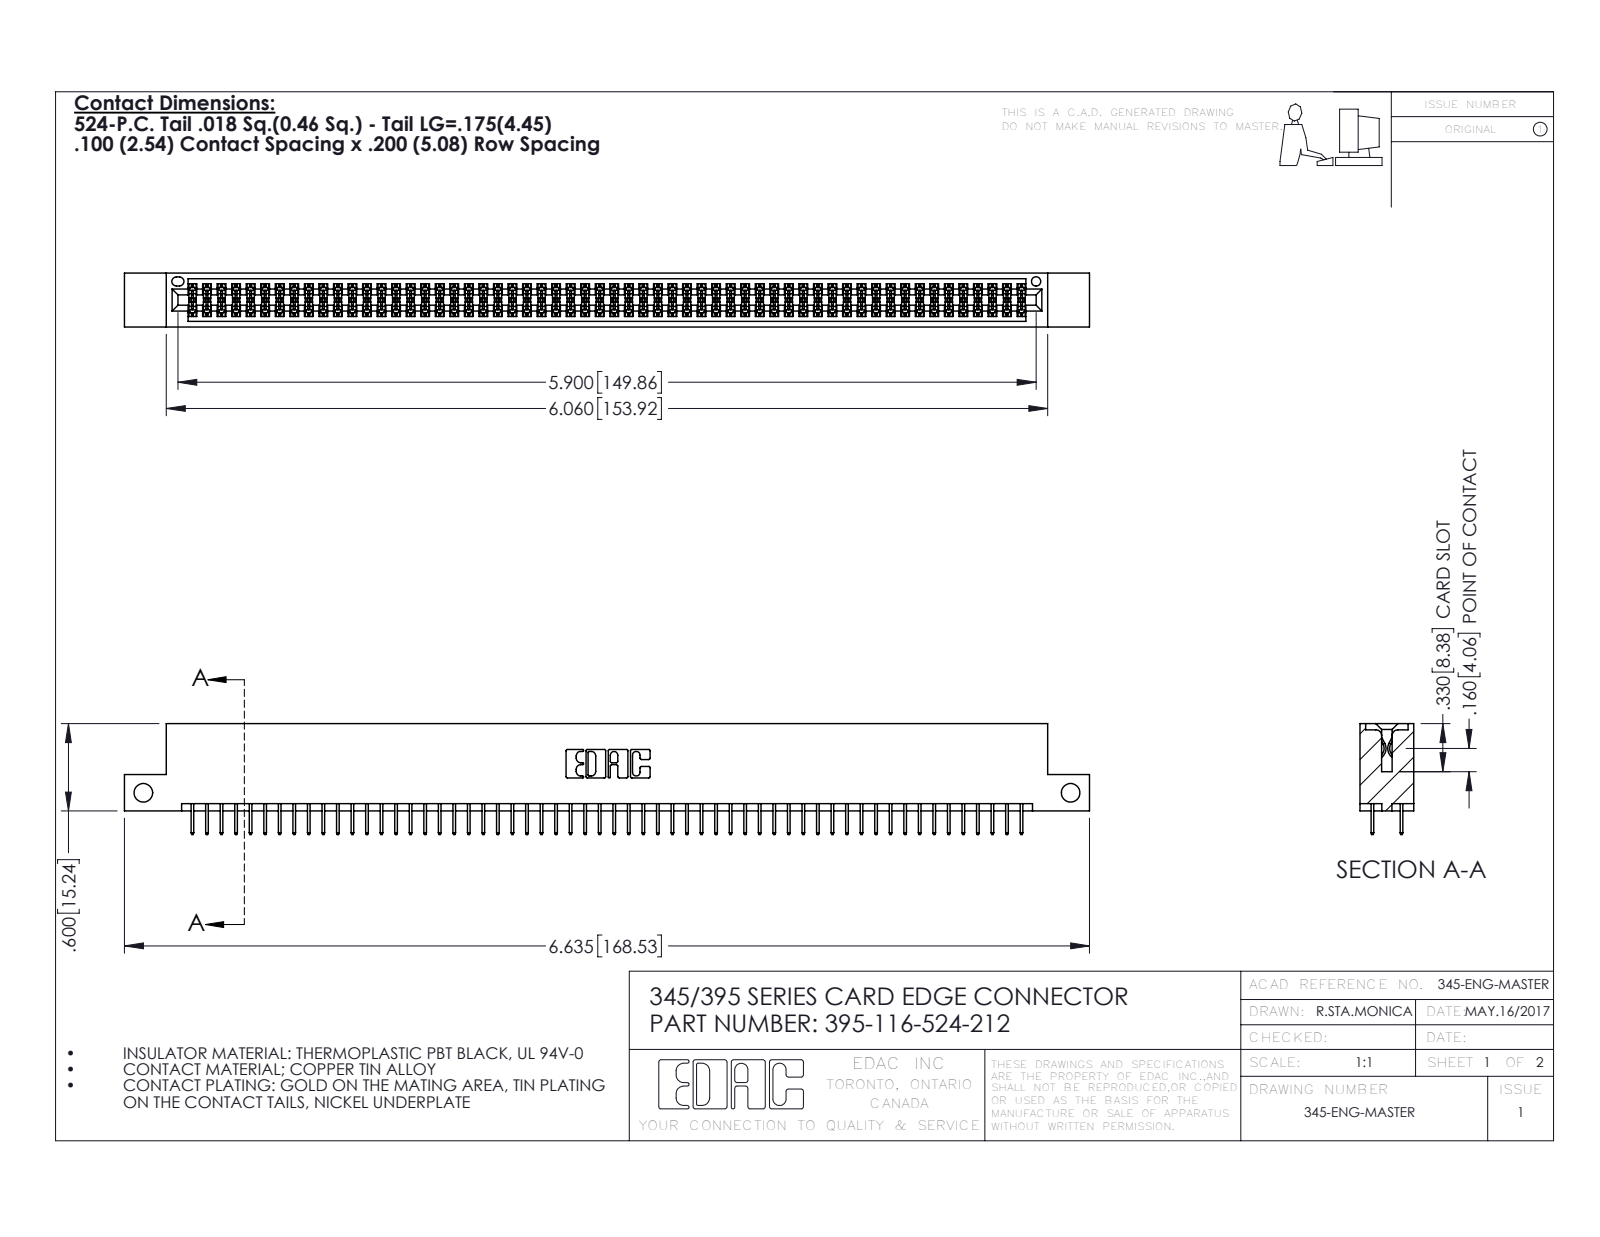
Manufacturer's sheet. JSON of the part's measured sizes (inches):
{"part_name": "345-292-001_345-293-124; 395-116-524-212; 345 Part_Flush Mounting Lugs - Side Mount", "step_written_by": "SolidWorks 2016 (CONFIG_CONTROL_DESIGN)", "units": "inches", "bodies": {"solids": 117, "faces": 6390, "planar": 4604, "cylindrical": 1786, "other": 0}, "overall_size": [6.635, 0.762, 0.37], "volume_in3": 0.992, "surface_area_in2": 36.8, "round_holes": [[0.128, 2], [0.064, 1]], "partial_cylinders_radius": [[0.006, 174], [0.01, 22], [0.007, 6], [0.031, 6], [0.026, 3], [0.014, 2], [0.019, 2], [0.022, 2]], "face_to_face_distances": [0.298, 0.072, 0.2, 0.37, 0.098, 0.272, 0.025, 0.225, 0.072, 0.175], "hole_center_spacings": [6.375]}
